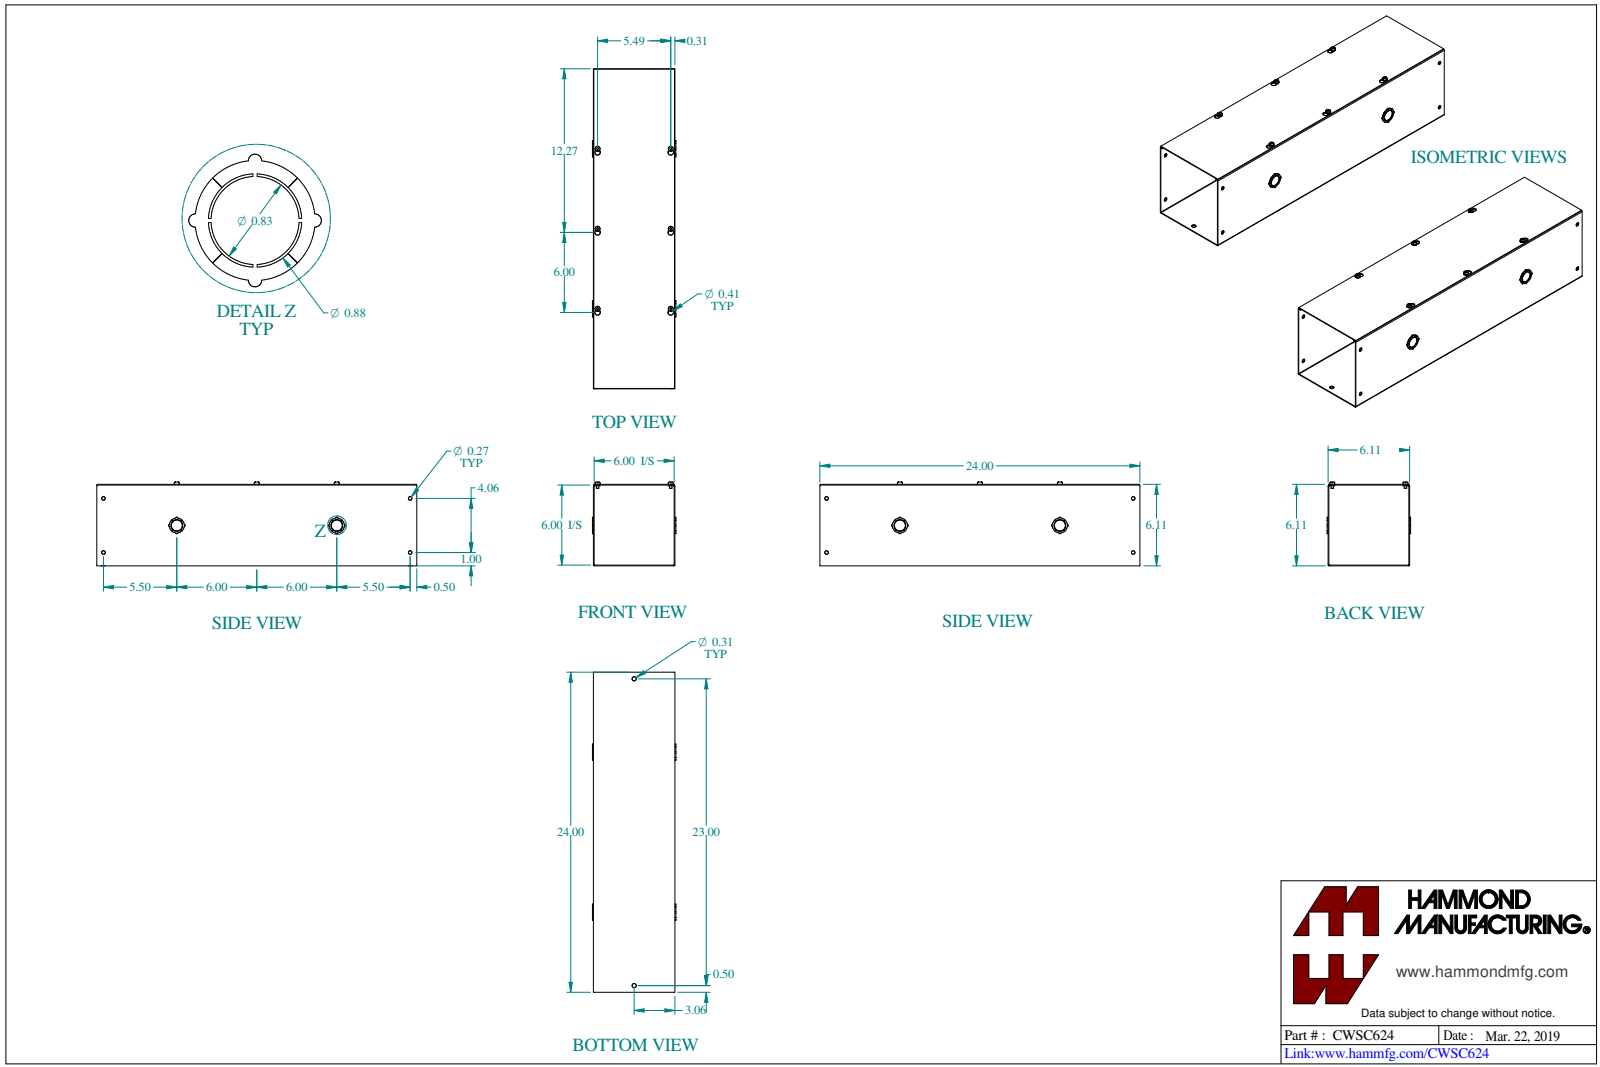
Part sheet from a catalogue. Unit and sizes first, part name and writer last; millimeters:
Units: millimetres
Overall size (bounding box): 609.6 × 159.7 × 159
Round holes (diameter × count): ⌀4.5 ×6, ⌀6.8 ×4, ⌀8 ×2, ⌀22.2 ×2
Round bosses / shafts (diameter × count): ⌀9.5 ×6, ⌀4.8 ×6, ⌀28.6 ×2, ⌀21 ×2
Partial cylindrical surfaces — rounded edges, fillets, slot ends (radius × count): R1.6 ×8, R3.2 ×6, R5.2 ×6, R0.7 ×4, R2.2 ×4, R1.6 ×2
Main face-to-face distances: 1.4, 153.8, 152.4, 155.3, 151, 2.9, 1.8, 3.3, 155.7, 157.1
Hole centre spacings: 148.9, 152.4, 156.1, 206.6, 300.3, 447.5, 449.9, 139.4
Volume: 563 200 mm³ · Surface area: 778 700 mm²
Bodies: 8 solids, 410 faces (186 planar, 188 cylindrical, 36 other)
Part name (STEP PRODUCT): CWSC624
STEP written by: SolidWorks 2023 (CONFIG_CONTROL_DESIGN)
